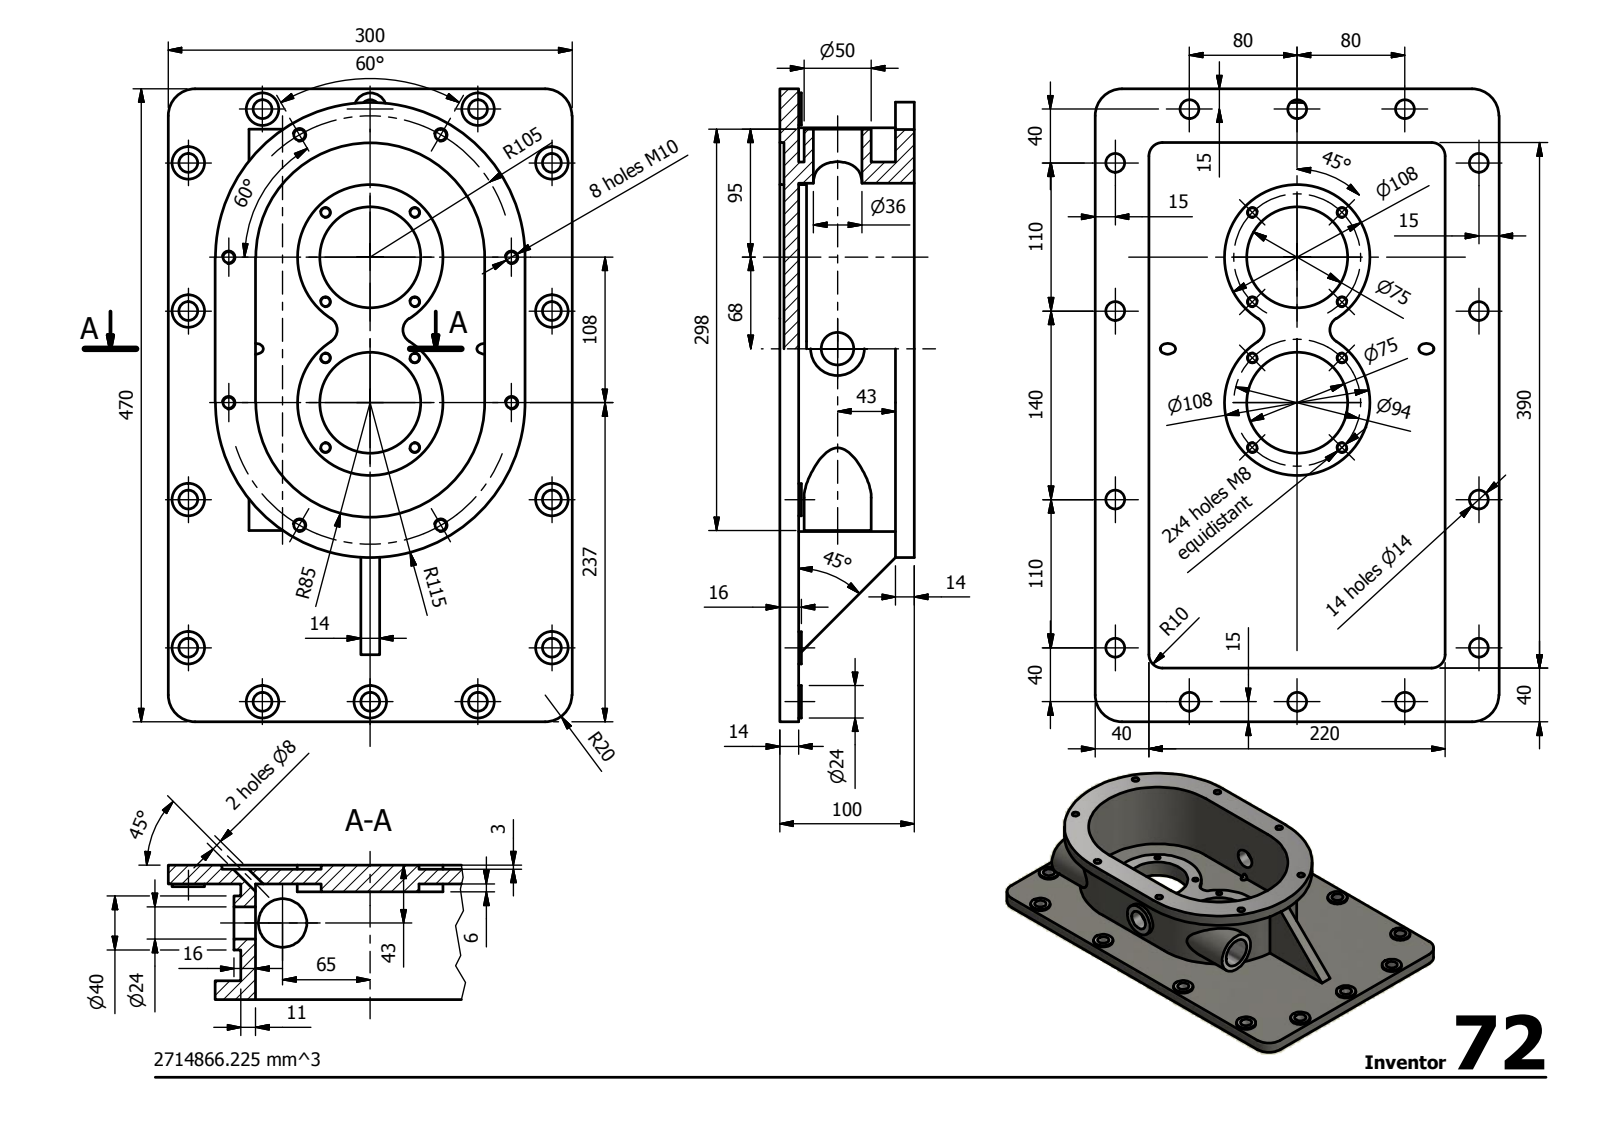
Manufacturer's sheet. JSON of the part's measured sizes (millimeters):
{"step_written_by": "Autodesk Inventor 2014 (AUTOMOTIVE_DESIGN)", "units": "millimeters", "bodies": {"solids": 1, "faces": 122, "planar": 43, "cylindrical": 79, "other": 0}, "overall_size": [470, 300, 100], "volume_mm3": 2715000, "surface_area_mm2": 506898, "round_holes": [[14, 14], [6.65, 8], [8.38, 8], [8, 2], [75, 2], [24, 1], [36, 1]], "round_bosses_or_shafts": [[24, 14], [108, 2], [50, 1], [40, 1]], "partial_cylinders_radius": [[10, 6], [20, 4], [85, 2], [96, 2], [115, 2]], "face_to_face_distances": [14, 11, 3, 86, 100, 97, 83, 72, 181, 54], "hole_center_spacings": [66.46, 79.09, 142.17, 105, 108, 250, 291.55, 60.83]}
